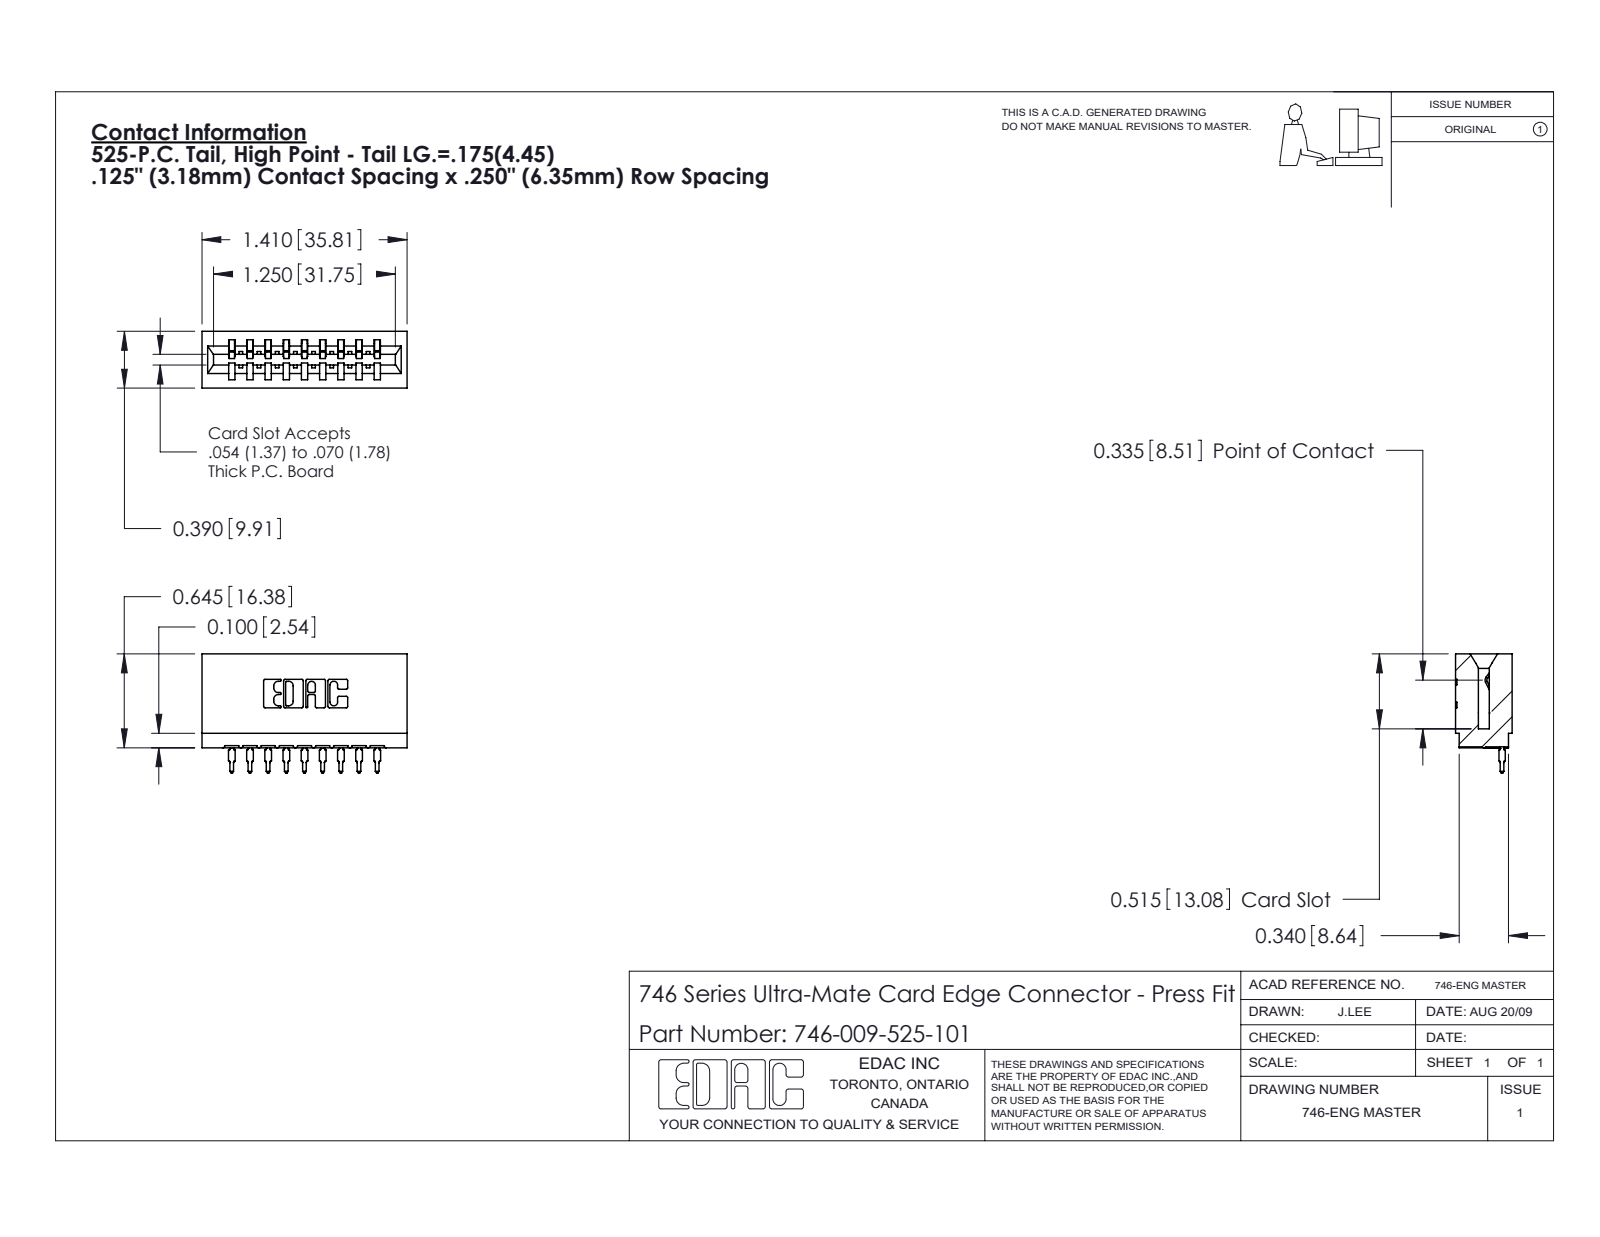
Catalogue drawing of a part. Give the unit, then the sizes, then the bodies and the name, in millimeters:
Units: millimetres
Overall size (bounding box): 35.8 × 20.8 × 9.9
Partial cylindrical surfaces — rounded edges, fillets, slot ends (radius × count): R0.3 ×22, R0.5 ×18, R0.4 ×10, R0.2 ×6, R0.8 ×6, R0.1 ×4, R0.3 ×4, R0.7 ×3
Main face-to-face distances: 6.4, 12.7, 1.1, 8.5, 3.2, 3.2, 7.4, 5.3, 1.4, 9.5
Volume: 3 950 mm³ · Surface area: 5 265 mm²
Bodies: 10 solids, 1069 faces (622 planar, 213 cylindrical, 234 other)
Part name (STEP PRODUCT): 746 Part_.515 Slot Depth - 01; 746-009-525-101; 746-292-001_525
STEP written by: SolidWorks 2020 (CONFIG_CONTROL_DESIGN)
